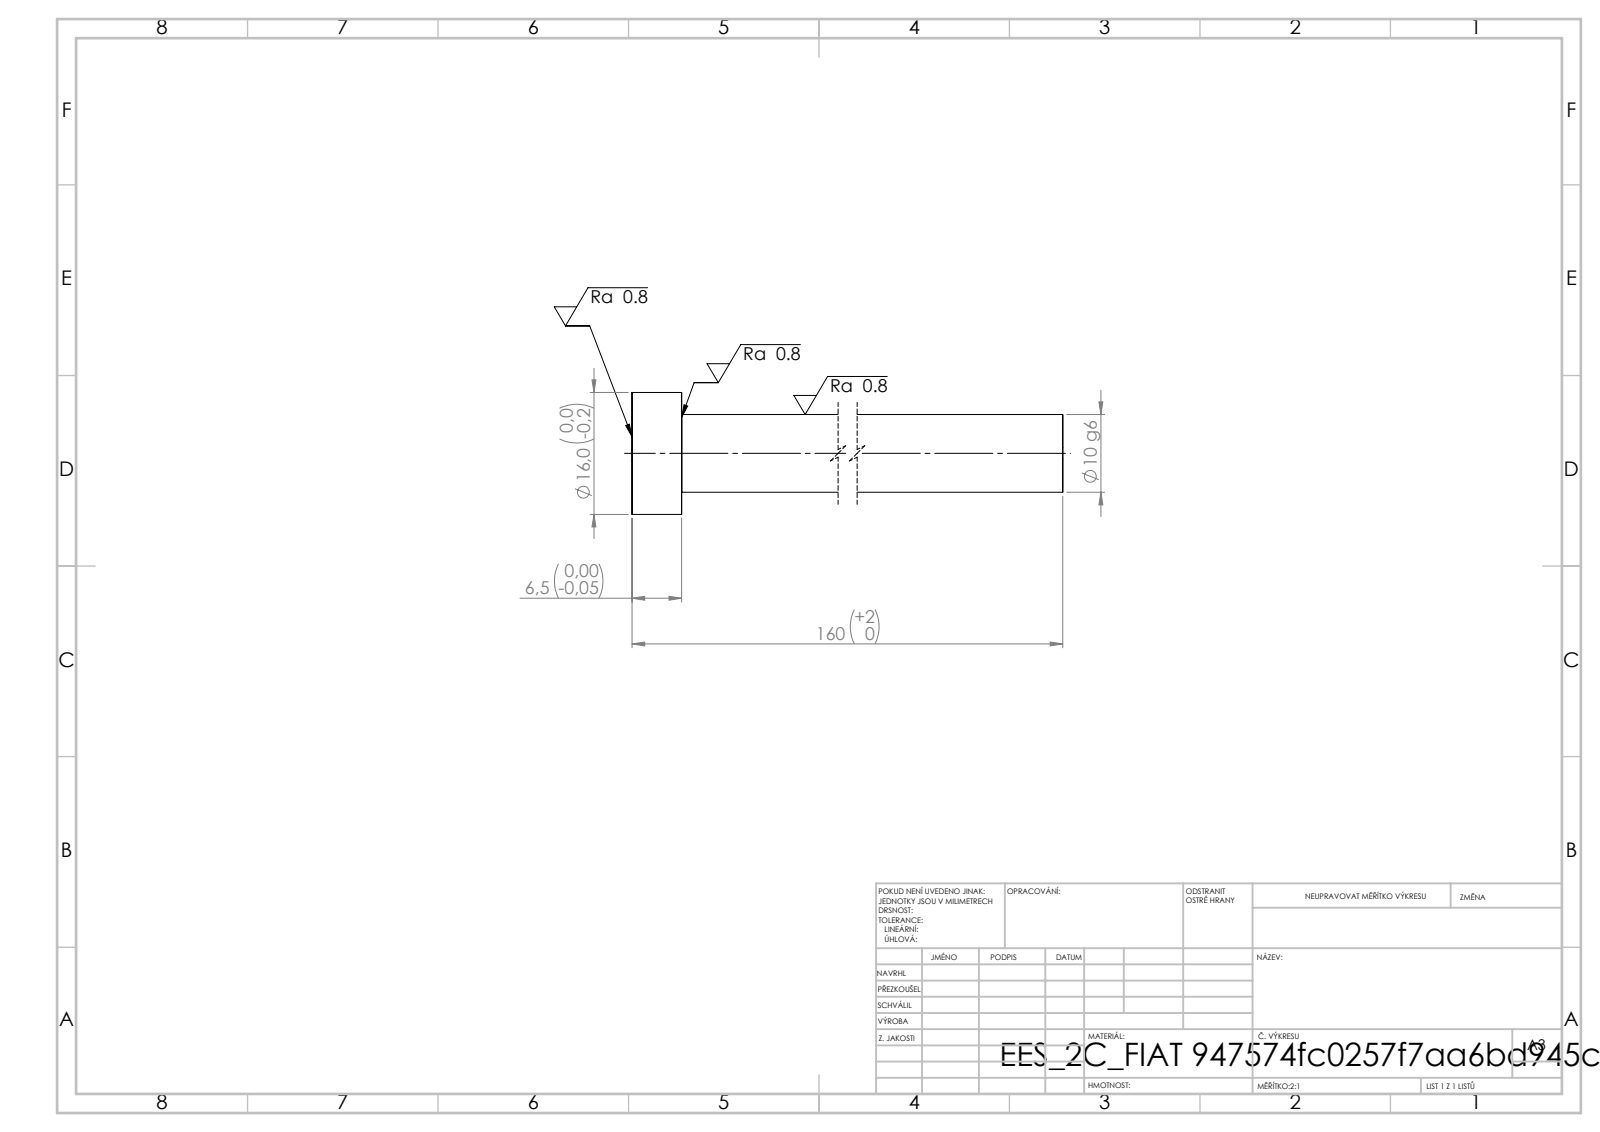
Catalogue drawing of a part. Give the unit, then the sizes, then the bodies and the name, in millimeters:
Units: millimetres
Overall size (bounding box): 160 × 16 × 16
Round bosses / shafts (diameter × count): ⌀16 ×1, ⌀10.2 ×1
Main face-to-face distances: 6.5, 160, 153.5
Volume: 13 850 mm³ · Surface area: 5 648 mm²
Bodies: 1 solid, 7 faces (3 planar, 4 cylindrical, 0 other)
STEP written by: SolidWorks 2019 (CONFIG_CONTROL_DESIGN)
